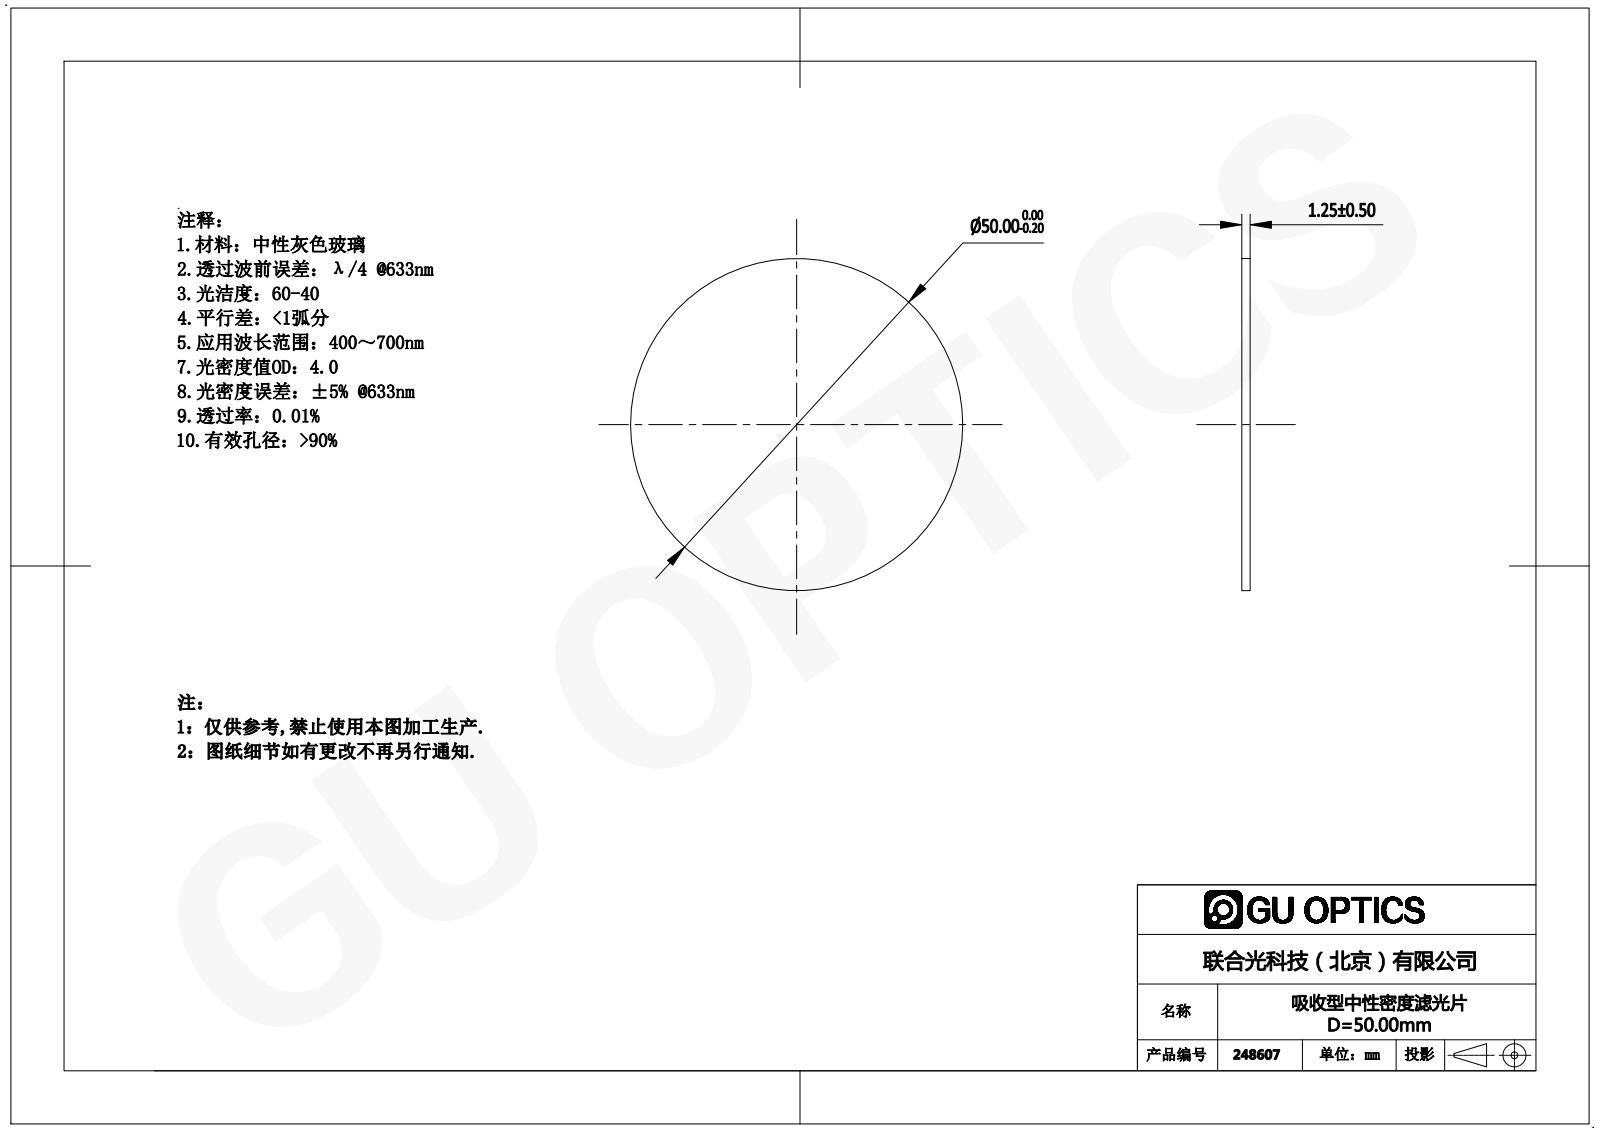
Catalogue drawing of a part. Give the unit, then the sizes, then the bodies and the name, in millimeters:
Units: millimetres
Overall size (bounding box): 50 × 50 × 1.25
Round bosses / shafts (diameter × count): ⌀50 ×1
Main face-to-face distances: 1.25
Volume: 2 454 mm³ · Surface area: 4 123 mm²
Bodies: 1 solid, 4 faces (2 planar, 2 cylindrical, 0 other)
Part name (STEP PRODUCT): 248607
STEP written by: SolidWorks 2016 (AUTOMOTIVE_DESIGN)
